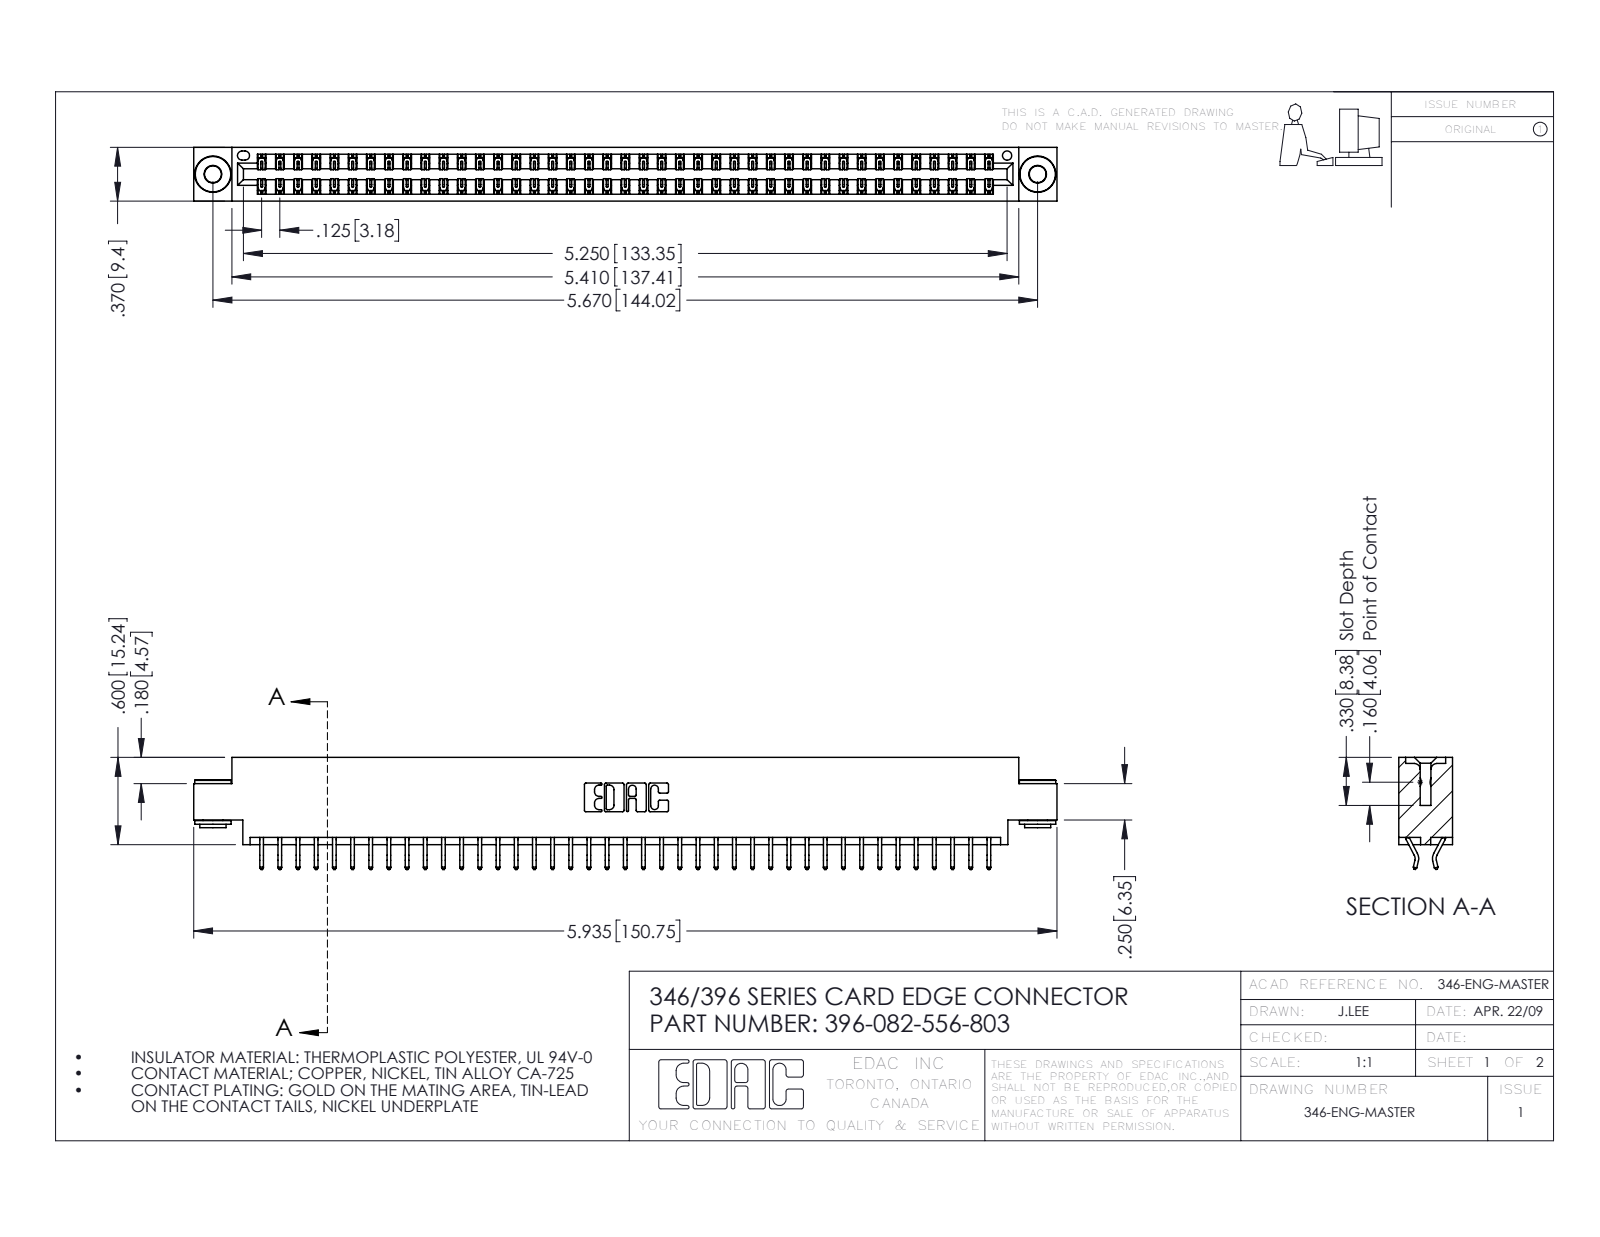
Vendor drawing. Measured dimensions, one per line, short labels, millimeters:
name: 345-292-001_556 Tail; 345-250-002_345-250-002-102; 346 Part_0.170 Offset - 0.156 Dia-TH; 396-082-556-803
written by: SolidWorks 2016 (CONFIG_CONTROL_DESIGN)
unit: mm
bodies: 85 solids, 4920 faces (3288 planar, 1624 cylindrical, 8 other)
size: 150.7 × 19.6 × 9.4
volume: 14 600 mm³; area: 20 310 mm²
holes: 2× ⌀2.9, 2× ⌀4, 1× ⌀1.6
bosses: 2× ⌀6.4, 2× ⌀4.6, 2× ⌀3.5
rounds: 123× R0.2, 22× R0.3, 6× R0.2, 6× R0.8, 3× R0.7, 2× R0.3, 2× R0.4, 2× R0.6
face distances: 1.2, 8.2, 9.4, 6.4, 0.6, 7, 1.8, 7.6, 3.8, 5.6
hole spacings: 6.2, 138.7, 144
